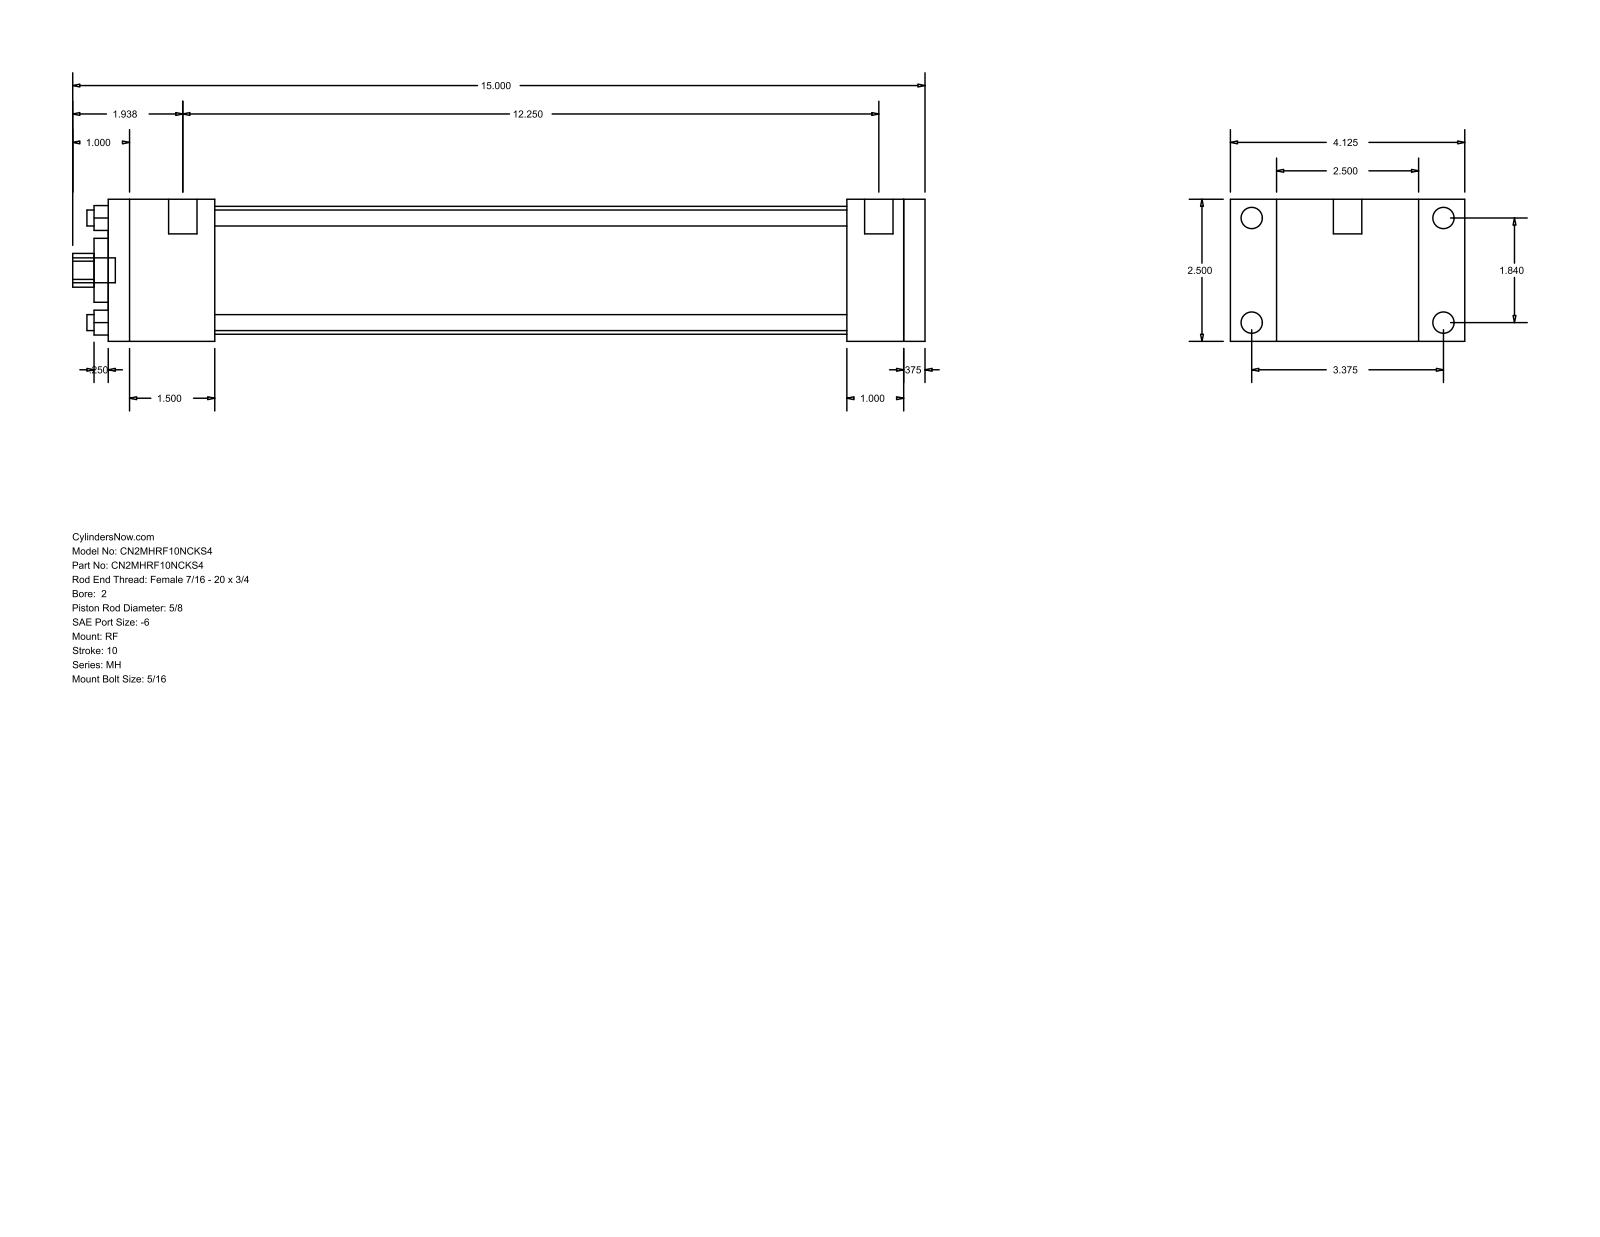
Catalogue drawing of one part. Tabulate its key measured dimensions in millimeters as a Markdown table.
| quantity | value |
| --- | --- |
| part name | MH_RF__0200_0.625 |
| STEP written by | GSSL Pune (CONFIG_CONTROL_DESIGN) |
| units | millimeters |
| bodies | 0 solids, 92 faces (64 planar, 28 cylindrical, 0 other) |
| overall size | 381 × 104.78 × 63.5 |
| round holes (diameter × count) | 7.14 × 4, 15.88 × 1, 28.57 × 1, 57.15 × 1 |
| round bosses / shafts (diameter × count) | 9.53 × 4, 5.56 × 4, 12.7 × 2, 11.11 × 1 |
| partial cylindrical surfaces (radius × count) | 7.54 × 1 |
| main face-to-face distances | 63.5, 365.12, 9.52, 355.6, 47.62, 330.19, 282.57, 307.98, 317.5, 25.41 |
| hole center spacings | 33.05, 46.74, 66.1 |
